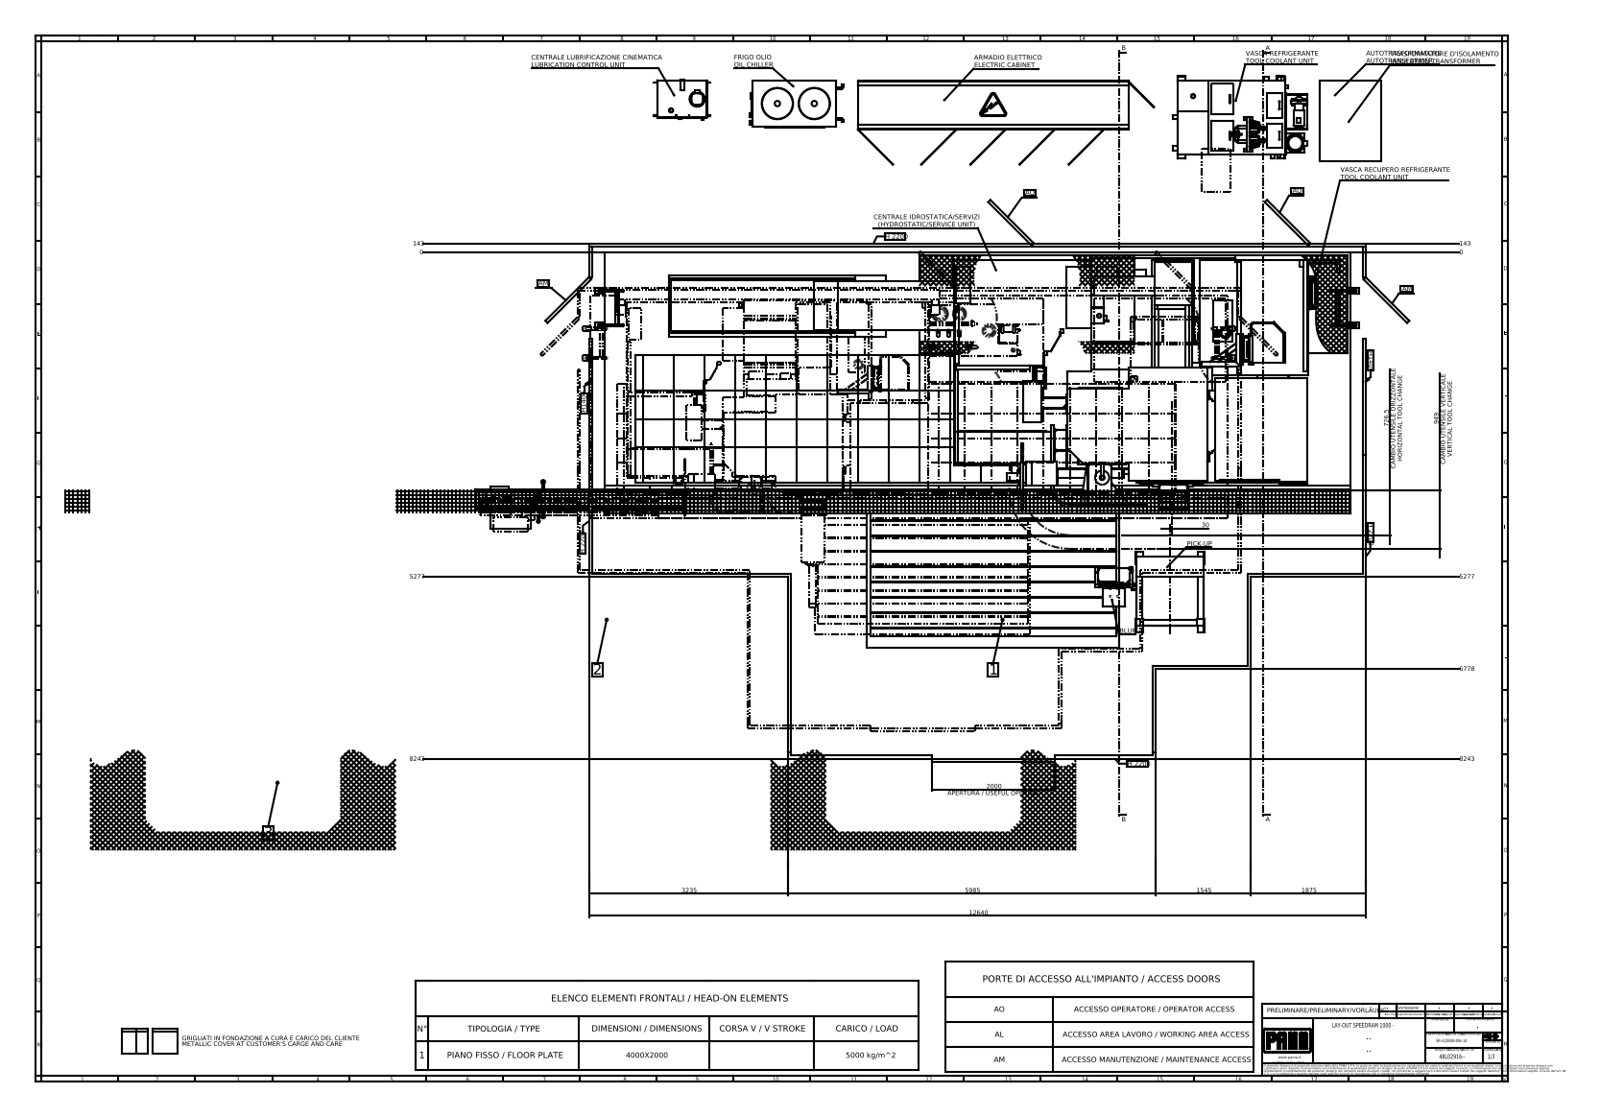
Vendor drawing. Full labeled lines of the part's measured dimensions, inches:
Part name (STEP PRODUCT): S002727_INTERASSE=1000; S002481_ANTE APERTE; S003251_ISO 50 - RIPOSO; S003219_BGB BARENO Ø130,4 Z=1200 (+8 more)
STEP written by: SolidWorks 2023 (AUTOMOTIVE_DESIGN)
Units: inches
Bodies: 401 solids, 6304 faces (4429 planar, 1421 cylindrical, 454 other)
Overall size (bounding box): 635.433 × 553.441 × 311.516
Volume: 25 140 000 in³ · Surface area: 2 482 000 in²
Round holes (diameter × count): ⌀1.378 ×64, ⌀2.74 ×63, ⌀1.465 ×18, ⌀1.181 ×9, ⌀0.512 ×8, ⌀0.551 ×8, ⌀0.315 ×6, ⌀0.492 ×4, ⌀2.231 ×4, ⌀2.362 ×4, ⌀1.008 ×3, ⌀1.969 ×3
Round bosses / shafts (diameter × count): ⌀1.669 ×18, ⌀0.787 ×14, ⌀1.575 ×11, ⌀0.354 ×10, ⌀2.165 ×8, ⌀2.61 ×7, ⌀2.362 ×6, ⌀1.378 ×6
Partial cylindrical surfaces — rounded edges, fillets, slot ends (radius × count): R0.197 ×128, R0.591 ×53, R0.315 ×52, R1.378 ×26, R0.236 ×25, R0.118 ×21, R0.157 ×21, R0.394 ×20
Main face-to-face distances: 78.74, 1.969, 49.094, 29.646, 0.197, 0.394, 550.63, 635.433, 104.331, 106.299
Hole centre spacings: 10.753, 19.685, 48.644, 29.843, 56.047, 39.37, 5.118, 10.236
